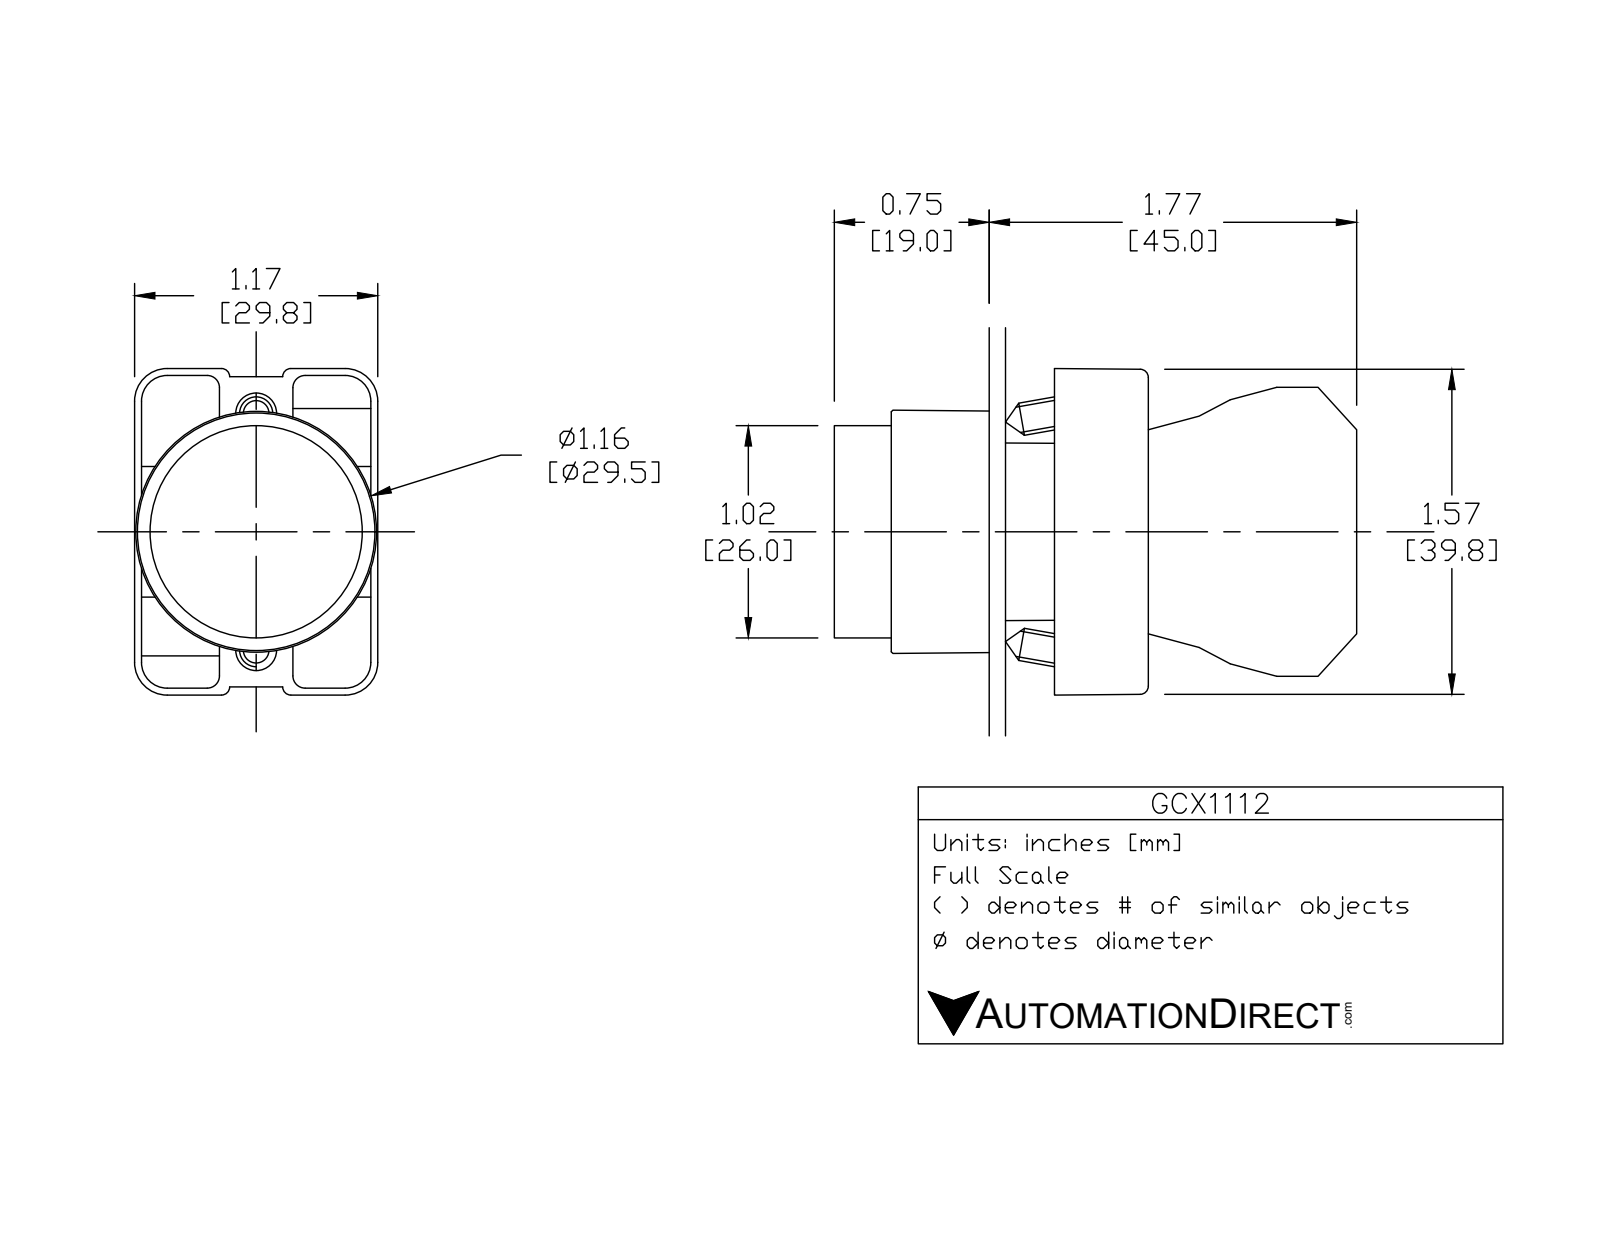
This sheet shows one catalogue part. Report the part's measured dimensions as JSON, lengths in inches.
{"part_name": "GCX1112 OPERATOR; ecx1029; GCX1112; ecx1040", "step_written_by": "SolidWorks 2016 (AUTOMOTIVE_DESIGN)", "units": "inches", "bodies": {"solids": 6, "faces": 383, "planar": 222, "cylindrical": 132, "other": 29}, "overall_size": [2.492, 1.581, 1.177], "volume_in3": 1.584, "surface_area_in2": 26.47, "round_holes": [[0.079, 2], [0.124, 2], [0.13, 2], [0.087, 1], [0.197, 1], [0.878, 1], [0.888, 1], [1.024, 1]], "round_bosses_or_shafts": [[0.157, 2], [1.175, 1], [1.004, 1], [0.945, 1], [0.856, 1], [0.78, 1]], "partial_cylinders_radius": [[0.059, 24], [0.041, 12], [0.124, 12], [0.157, 12], [0.039, 4], [0.128, 2], [0.02, 1], [0.063, 1]], "face_to_face_distances": [0.579, 0.033, 1.193, 0.031, 0.472, 0.72, 0.276, 0.689, 0.598, 1.161], "hole_center_spacings": [0.236, 0.544, 0.472, 0.49]}
